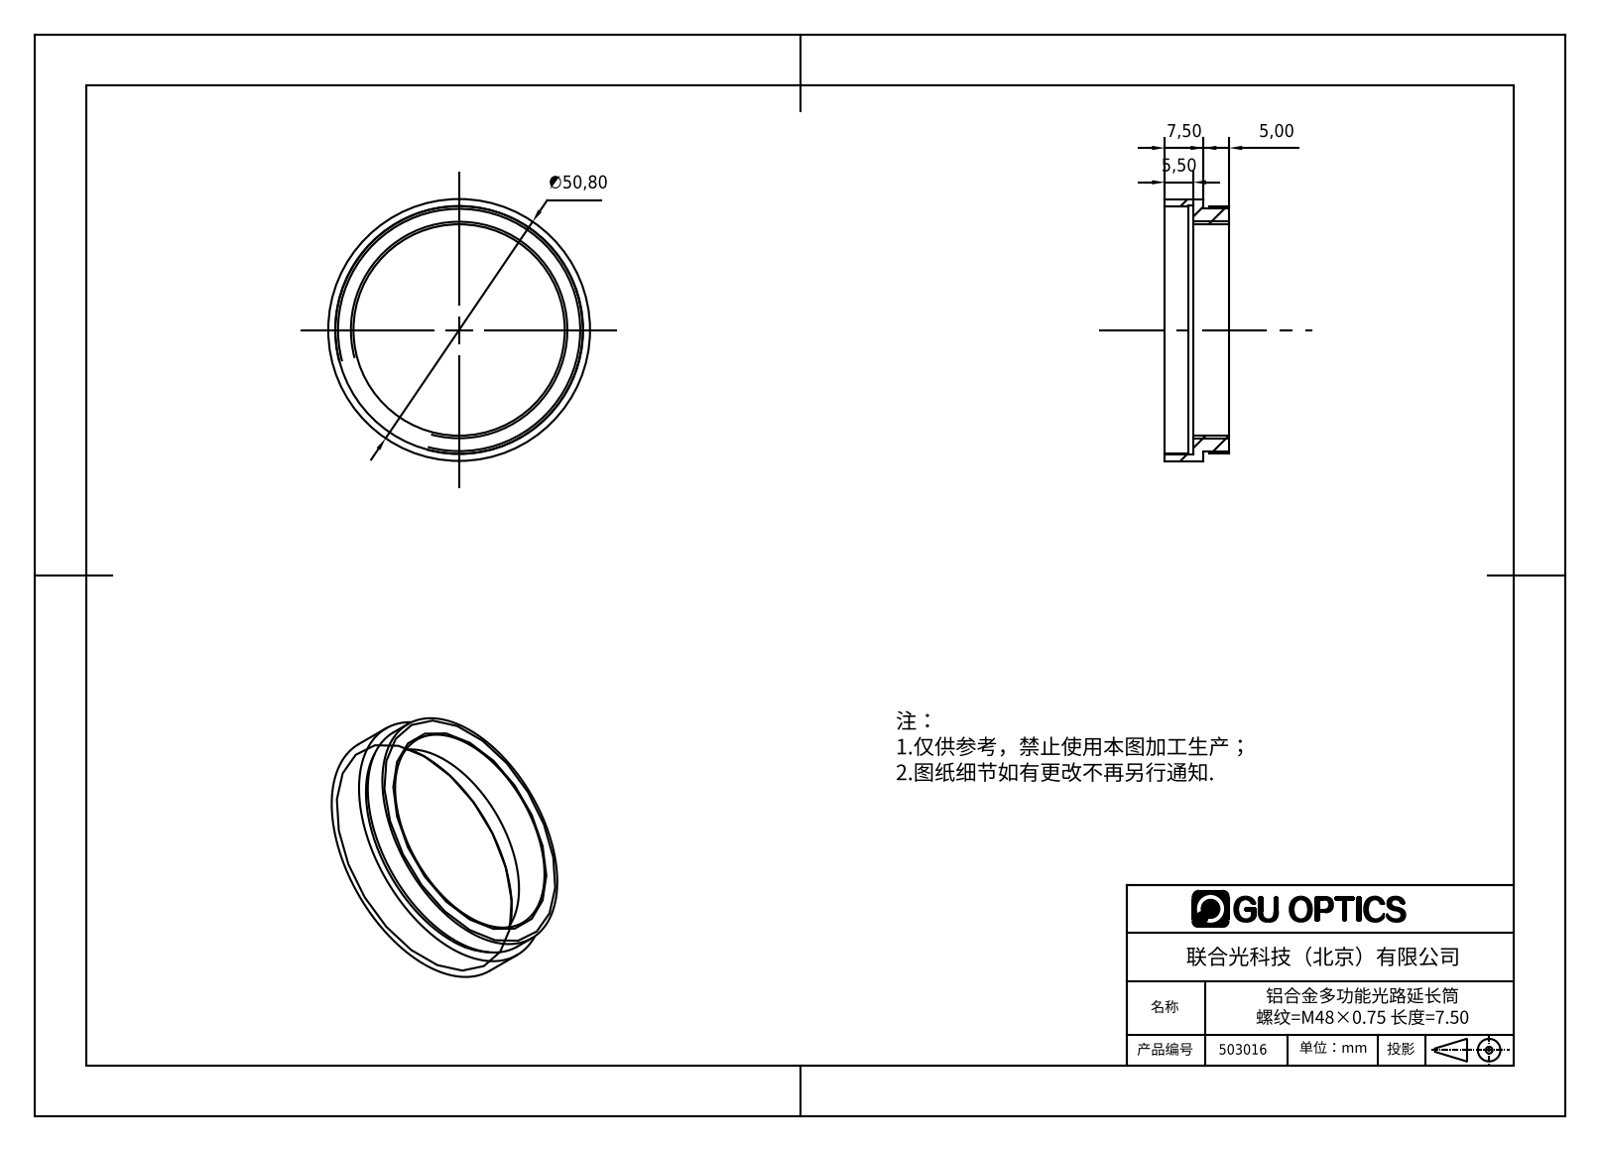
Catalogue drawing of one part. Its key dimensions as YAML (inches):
part_name: "503016"
step_written_by: "SolidWorks 2016 (AUTOMOTIVE_DESIGN)"
units: inches
bodies: {solids: 1, faces: 18, planar: 6, cylindrical: 12, other: 0}
overall_size: [2, 2, 0.492]
volume: 0.303
surface_area: 8.172
round_holes:
  - {diameter: 1.614, count: 1}
  - {diameter: 1.89, count: 1}
  - {diameter: 1.898, count: 1}
round_bosses_or_shafts:
  - {diameter: 2, count: 1}
  - {diameter: 1.85, count: 1}
face_to_face_distances: [0.276, 0.079, 0.197, 0.217, 0.295, 0.492, 0.039, 0.118, 0.157, 0.335]
